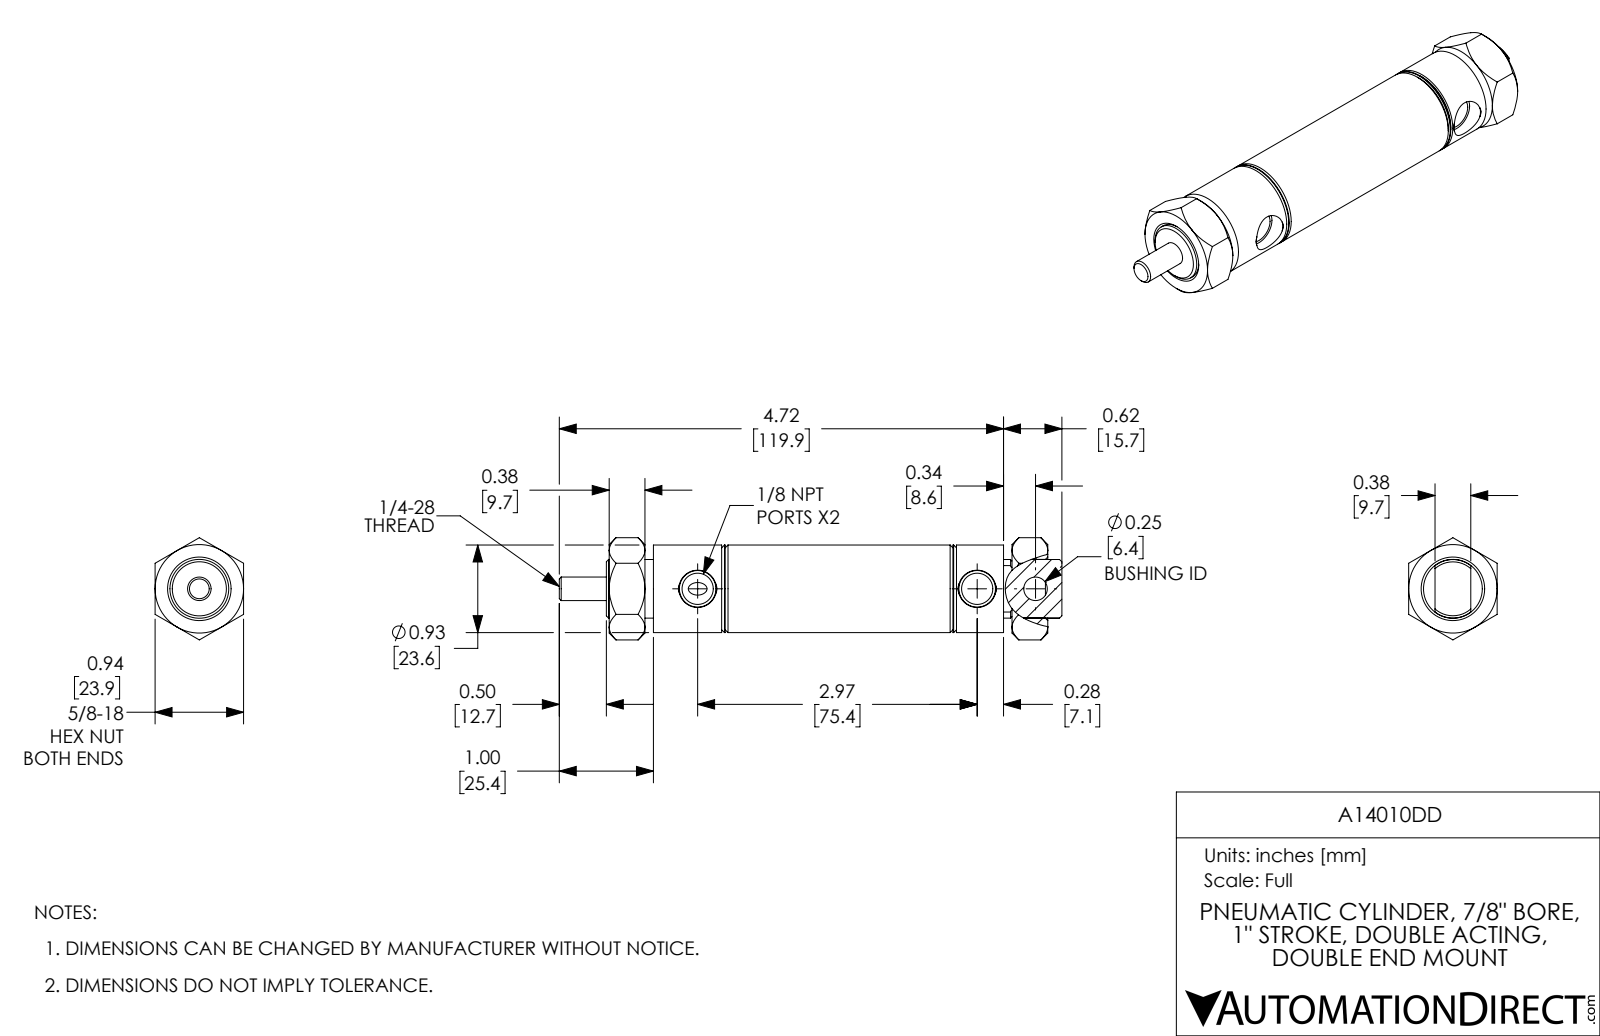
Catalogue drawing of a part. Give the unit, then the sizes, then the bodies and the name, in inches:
Units: inches
Overall size (bounding box): 5.34 × 1.085 × 0.94
Round holes (diameter × count): ⌀0.25 ×2, ⌀0.332 ×2, ⌀0.625 ×1, ⌀0.875 ×1
Round bosses / shafts (diameter × count): ⌀0.93 ×1, ⌀0.623 ×1, ⌀0.562 ×1
Main face-to-face distances: 0.94, 0.5, 0.47, 4.19, 0.38, 1, 2.722, 1.5, 0.998, 0.28
Hole centre spacings: 0.62, 2.97, 3.59
Volume: 2.535 in³ · Surface area: 32.83 in²
Bodies: 4 solids, 137 faces (35 planar, 38 cylindrical, 64 other)
Part name (STEP PRODUCT): A14010DD; A14010DD_Mounting Nut_D-9; A14010DD-Rod; A14010DD-MainBody
STEP written by: SolidWorks 2017 (AUTOMOTIVE_DESIGN)
